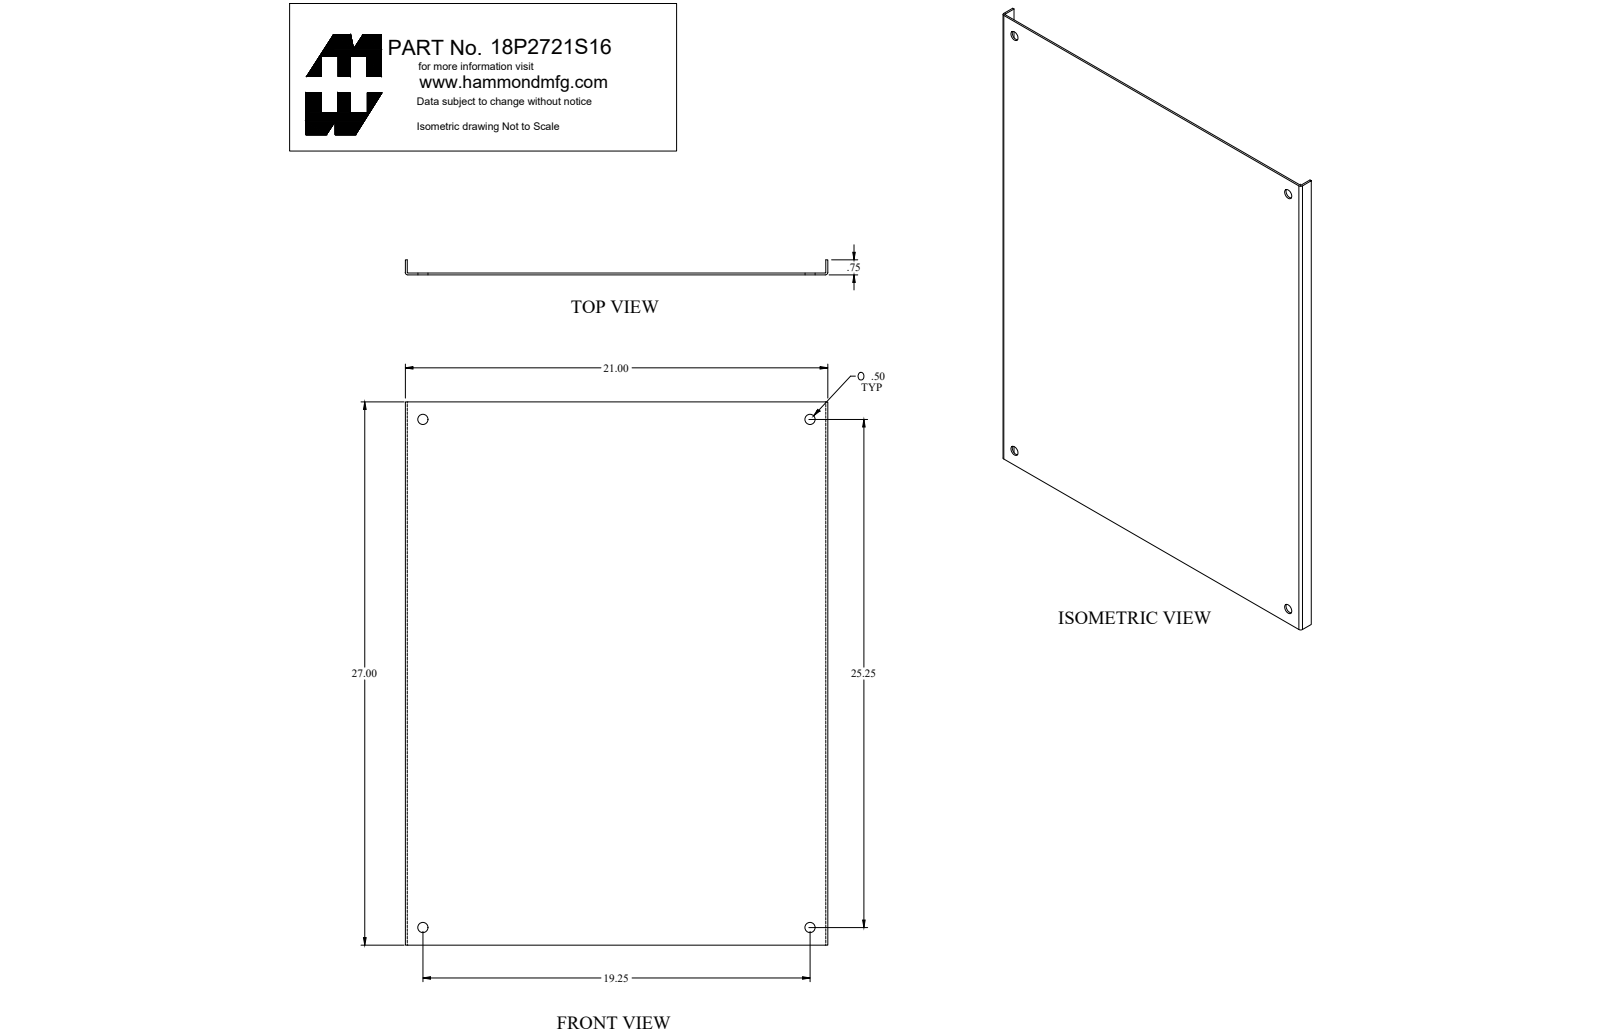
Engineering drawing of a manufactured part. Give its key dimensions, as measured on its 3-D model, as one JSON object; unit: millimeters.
{"part_name": "18P2721S16_Default", "step_written_by": "SolidWorks 2018 (CONFIG_CONTROL_DESIGN)", "units": "millimeters", "bodies": {"solids": 1, "faces": 22, "planar": 10, "cylindrical": 12, "other": 0}, "overall_size": [685.8, 533.4, 19.1], "volume_mm3": 933700, "surface_area_mm2": 780600, "round_holes": [[12.7, 4]], "partial_cylinders_radius": [[0.8, 2], [3.2, 2]], "face_to_face_distances": [2.4, 531, 533.4, 528.6, 19.1, 16.6, 685.8], "hole_center_spacings": [489, 641.4, 806.5]}
